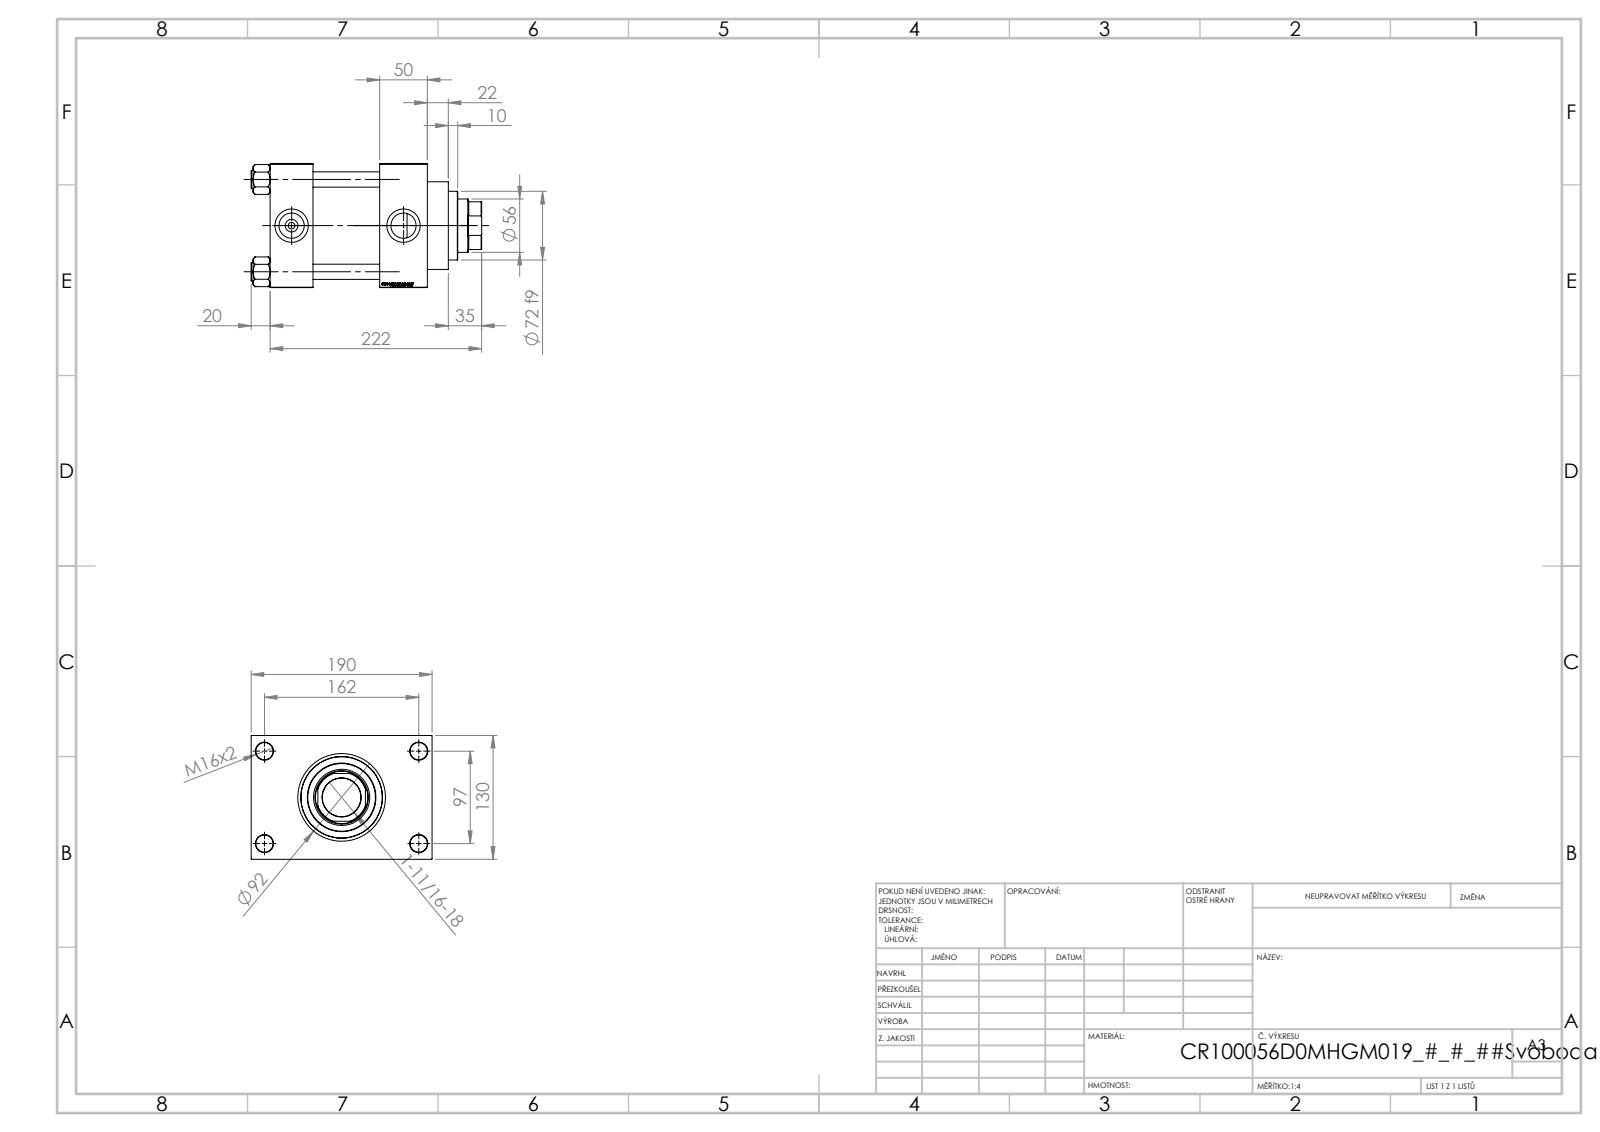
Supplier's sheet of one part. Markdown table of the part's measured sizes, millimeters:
| quantity | value |
| --- | --- |
| part name | V215CR_VCP_D; NUT_M5_D; V215CR_D_TYCINKA; V215CR_D_Body (+1 more) |
| STEP written by | SolidWorks 2019 (CONFIG_CONTROL_DESIGN) |
| units | millimeters |
| bodies | 11 solids, 1151 faces (545 planar, 88 cylindrical, 518 other) |
| overall size | 242 × 190 × 130 |
| volume | 2 624 000 mm³ |
| surface area | 361 339 mm² |
| round holes (diameter × count) | 16 × 4, 18 × 4, 7 × 2, 26.44 × 2, 35 × 2, 40.5 × 1, 56 × 1, 59 × 1, 76 × 1, 85.5 × 1, 100 × 1 |
| round bosses / shafts (diameter × count) | 19 × 4, 106 × 1, 92 × 1, 72 × 1 |
| partial cylindrical surfaces (radius × count) | 27 × 1 |
| main face-to-face distances | 130, 70, 120, 50, 45, 115, 165, 30, 160, 69 |
| hole center spacings | 32.55, 68.52, 94.41, 96.9, 102.27, 129.45, 161.73, 97 |
